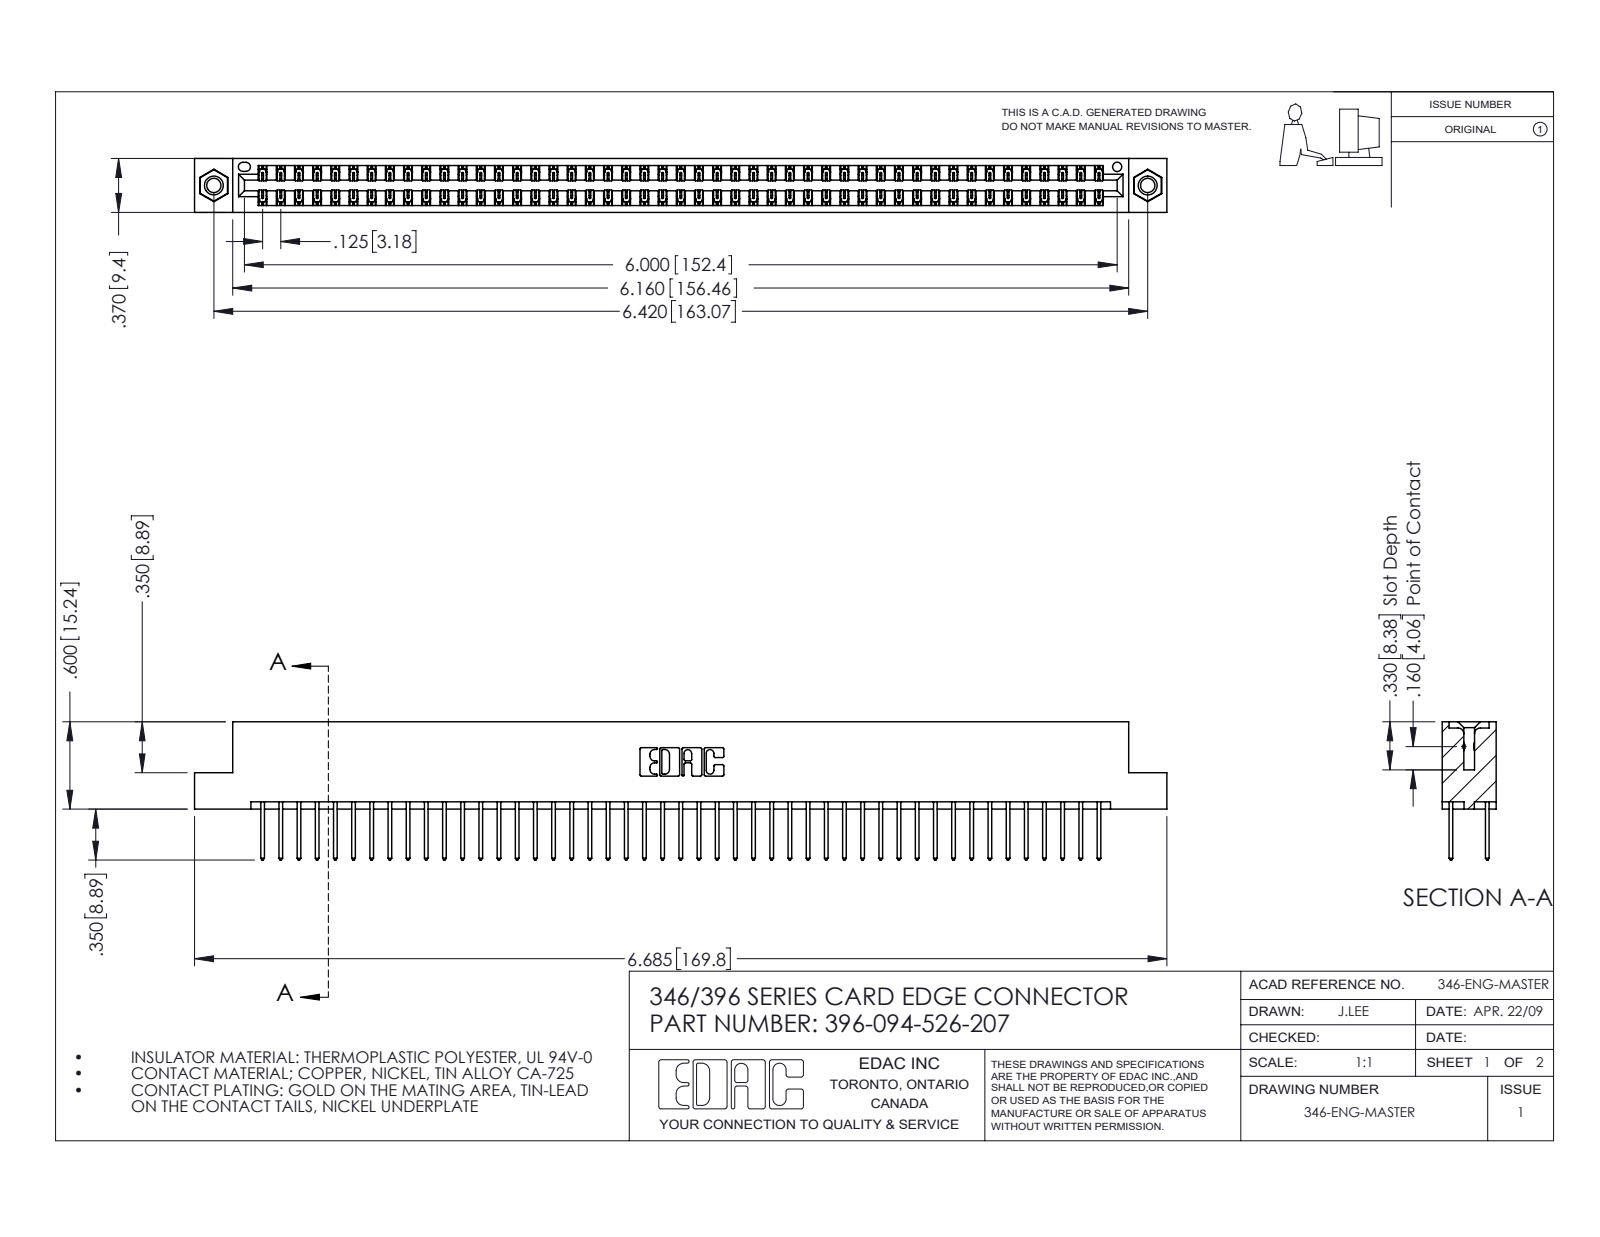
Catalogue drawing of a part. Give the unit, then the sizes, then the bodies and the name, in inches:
Units: inches
Overall size (bounding box): 6.685 × 0.95 × 0.37
Round holes (diameter × count): ⌀0.098 ×2, ⌀0.125 ×2, ⌀0.156 ×2, ⌀0.064 ×1
Round bosses / shafts (diameter × count): ⌀0.155 ×2
Partial cylindrical surfaces — rounded edges, fillets, slot ends (radius × count): R0.006 ×141, R0.01 ×94, R0.01 ×22, R0.007 ×6, R0.031 ×6, R0.026 ×3, R0.014 ×2, R0.022 ×2
Main face-to-face distances: 0.048, 0.322, 0.25, 0.37, 0.072, 0.298, 0.025, 0.275, 0.148, 0.222
Hole centre spacings: 0.246, 6.211, 6.42
Volume: 1.021 in³ · Surface area: 36.9 in²
Bodies: 97 solids, 5070 faces (3398 planar, 1656 cylindrical, 16 other)
Part name (STEP PRODUCT): 346 Part_Flush Mounting Lugs - 0.156 Dia-TI; 345-292-001_345-293-126; 396-094-526-207; 345-250-001_345-250-005-103
STEP written by: SolidWorks 2016 (CONFIG_CONTROL_DESIGN)
